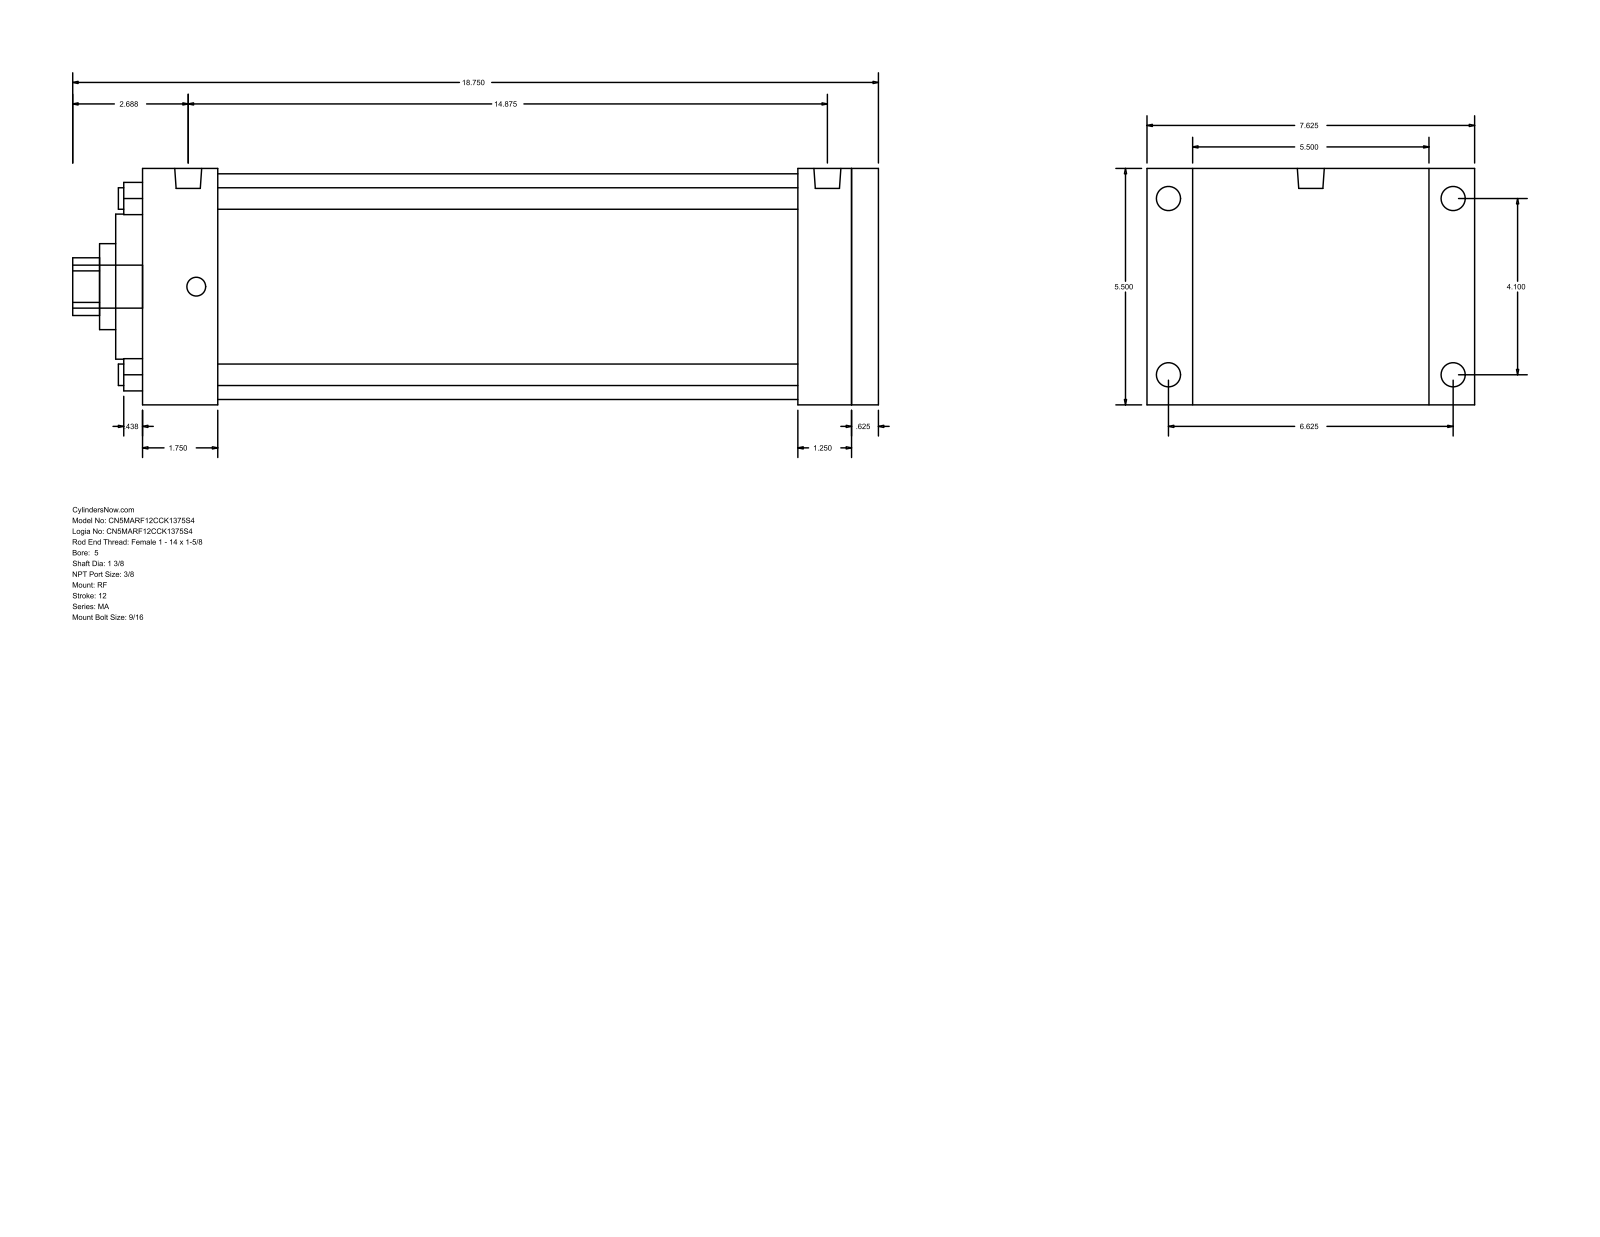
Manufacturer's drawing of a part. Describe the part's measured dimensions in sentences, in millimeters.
The part is named "MA_RF__0500_1.375". Its 3-D file was written by "GSSL Pune (CONFIG_CONTROL_DESIGN)". It is 0 solids with 94 faces: 65 planar, 29 cylindrical and 0 other. Overall it measures 476.25 by 193.68 by 139.7 millimeters. Round holes: 4 of diameter 12.7, 1 of diameter 34.92, 1 of diameter 50.8, 1 of diameter 85.72, 1 of diameter 133.35. Round bosses or shafts: 4 of diameter 14.29, 4 of diameter 11.11, 2 of diameter 15.93, 1 of diameter 25.4. Partial cylindrical surfaces (rounded edges, fillets, slot ends): 1 of radius 17.06. The main face-to-face distances are 139.7, 434.98, 15.87, 419.11, 44.45, 374.66, 390.53, 387.35, 342.9, 31.76. The hole center spacings are 73.64, 104.14, 147.28.
